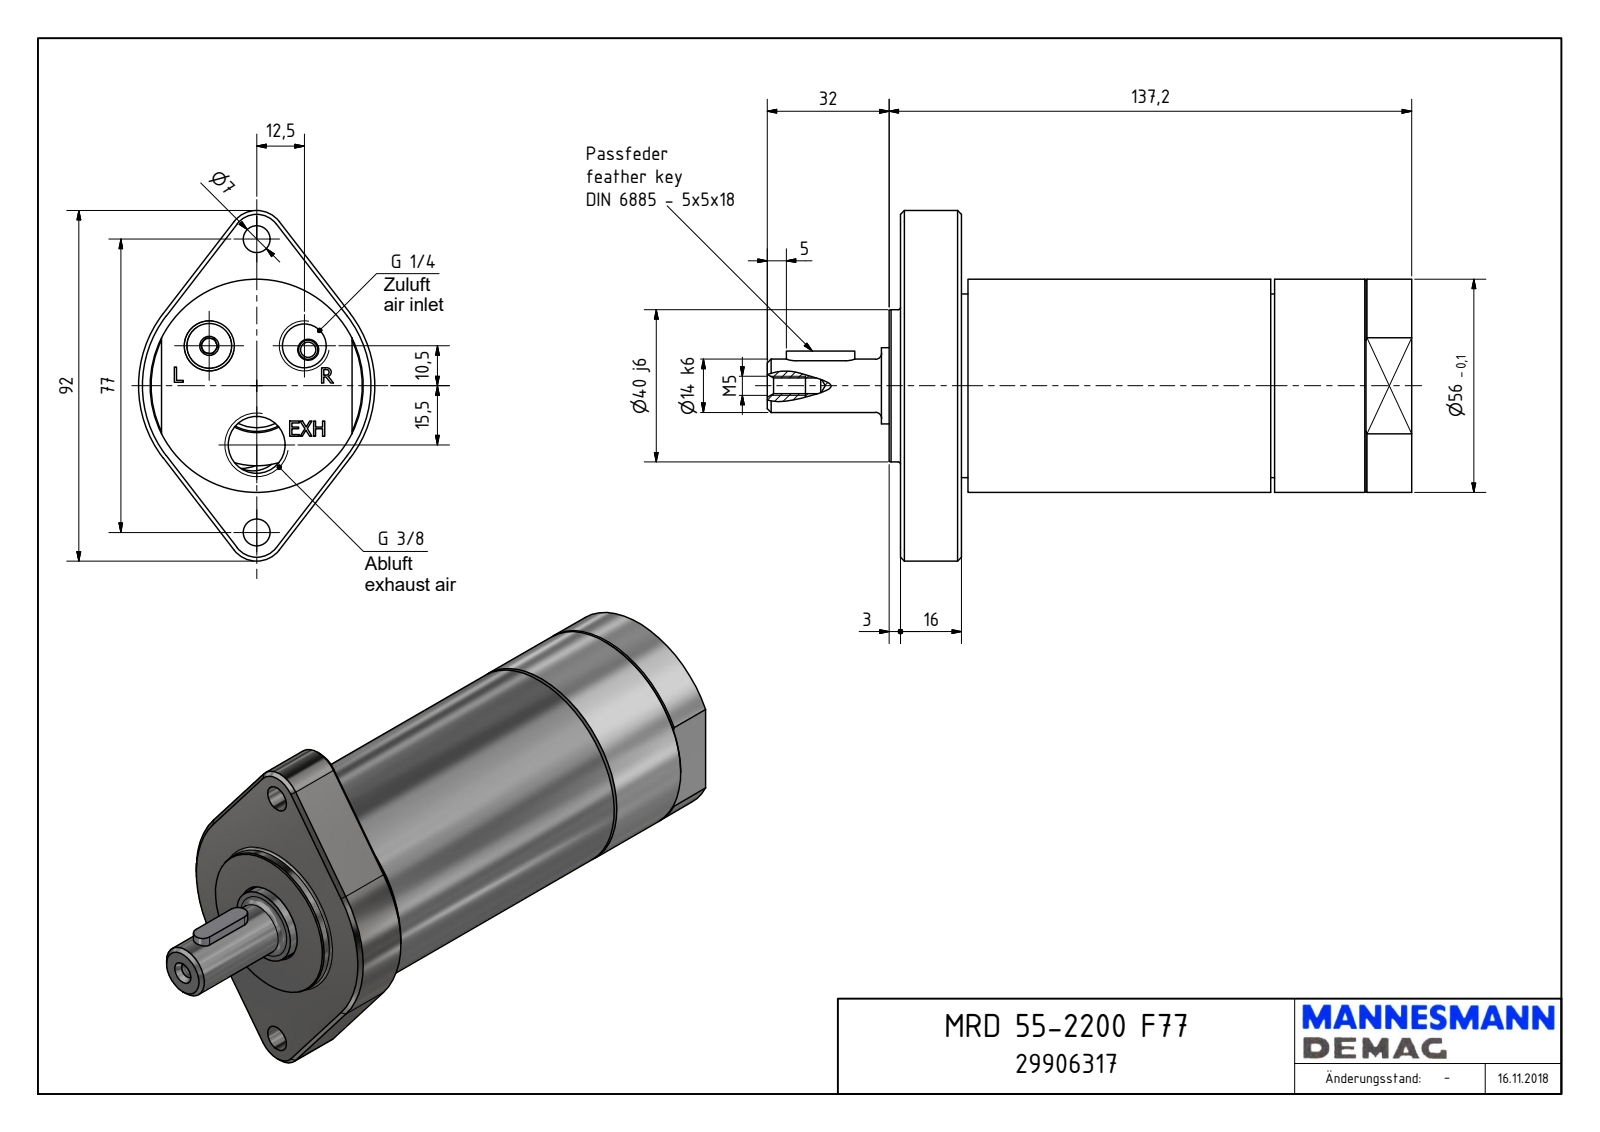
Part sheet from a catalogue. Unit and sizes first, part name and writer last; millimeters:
Units: millimetres
Overall size (bounding box): 169.2 × 92 × 62
Round holes (diameter × count): ⌀7 ×2, ⌀4 ×1, ⌀4.13 ×1, ⌀11.45 ×1, ⌀14.95 ×1, ⌀21 ×1, ⌀21.25 ×1, ⌀23.54 ×1, ⌀26 ×1, ⌀48.38 ×1
Round bosses / shafts (diameter × count): ⌀56 ×1, ⌀48.18 ×1, ⌀40 ×1, ⌀19.95 ×1, ⌀14 ×1
Partial cylindrical surfaces — rounded edges, fillets, slot ends (radius × count): R2.5 ×2, R7.5 ×2, R31 ×1
Main face-to-face distances: 134.2, 16, 118.2, 3, 19, 137.2, 20.7, 17.7, 1.7, 116.5
Hole centre spacings: 16.32, 28.85, 30.66, 38.5, 50.57, 15.5, 23, 25
Volume: 352 051 mm³ · Surface area: 39 632 mm²
Bodies: 1 solid, 191 faces (114 planar, 28 cylindrical, 49 other)
Part name (STEP PRODUCT): MRD 55-2200 F77_29906317
STEP written by: Autodesk Inventor 2018 (AUTOMOTIVE_DESIGN)
